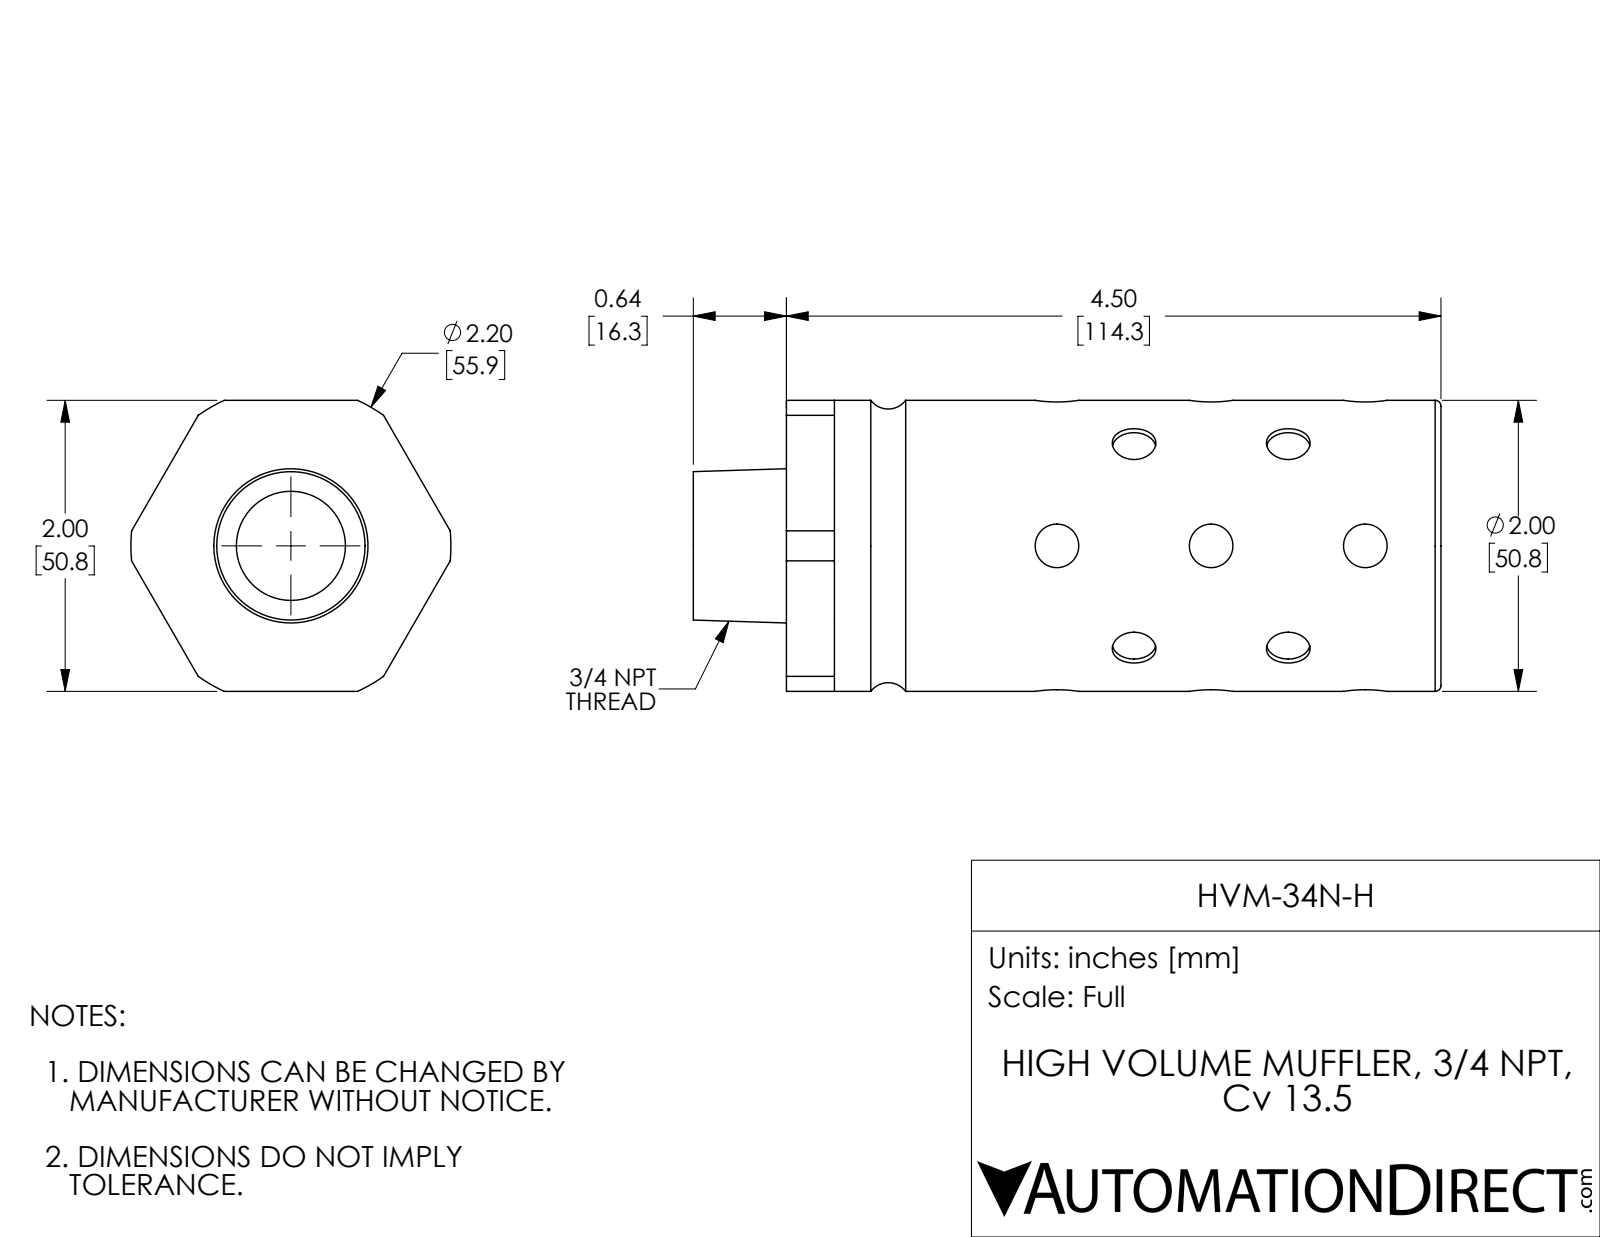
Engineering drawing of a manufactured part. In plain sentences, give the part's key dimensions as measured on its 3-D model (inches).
The part is named "HVM-34N-H". Its 3-D file was written by "SolidWorks 2017 (AUTOMOTIVE_DESIGN)". It is 1 solid with 97 faces: 36 planar, 53 cylindrical and 8 other. Overall it measures 5.14 by 2.2 by 2 inches. Its volume is 12.49 cubic inches and its surface area 49.73 square inches. Round holes: 14 of diameter 0.3, 1 of diameter 0.75. Round bosses or shafts: 1 of diameter 2. Partial cylindrical surfaces (rounded edges, fillets, slot ends): 1 of radius 1.1. The main face-to-face distances are 4.5, 2, 1.9, 4.25, 0.25, 0.05, 1.95, 0.64, 4.89, 5.14. The hole center spacings are 1.06, 1.06, 2.12.
